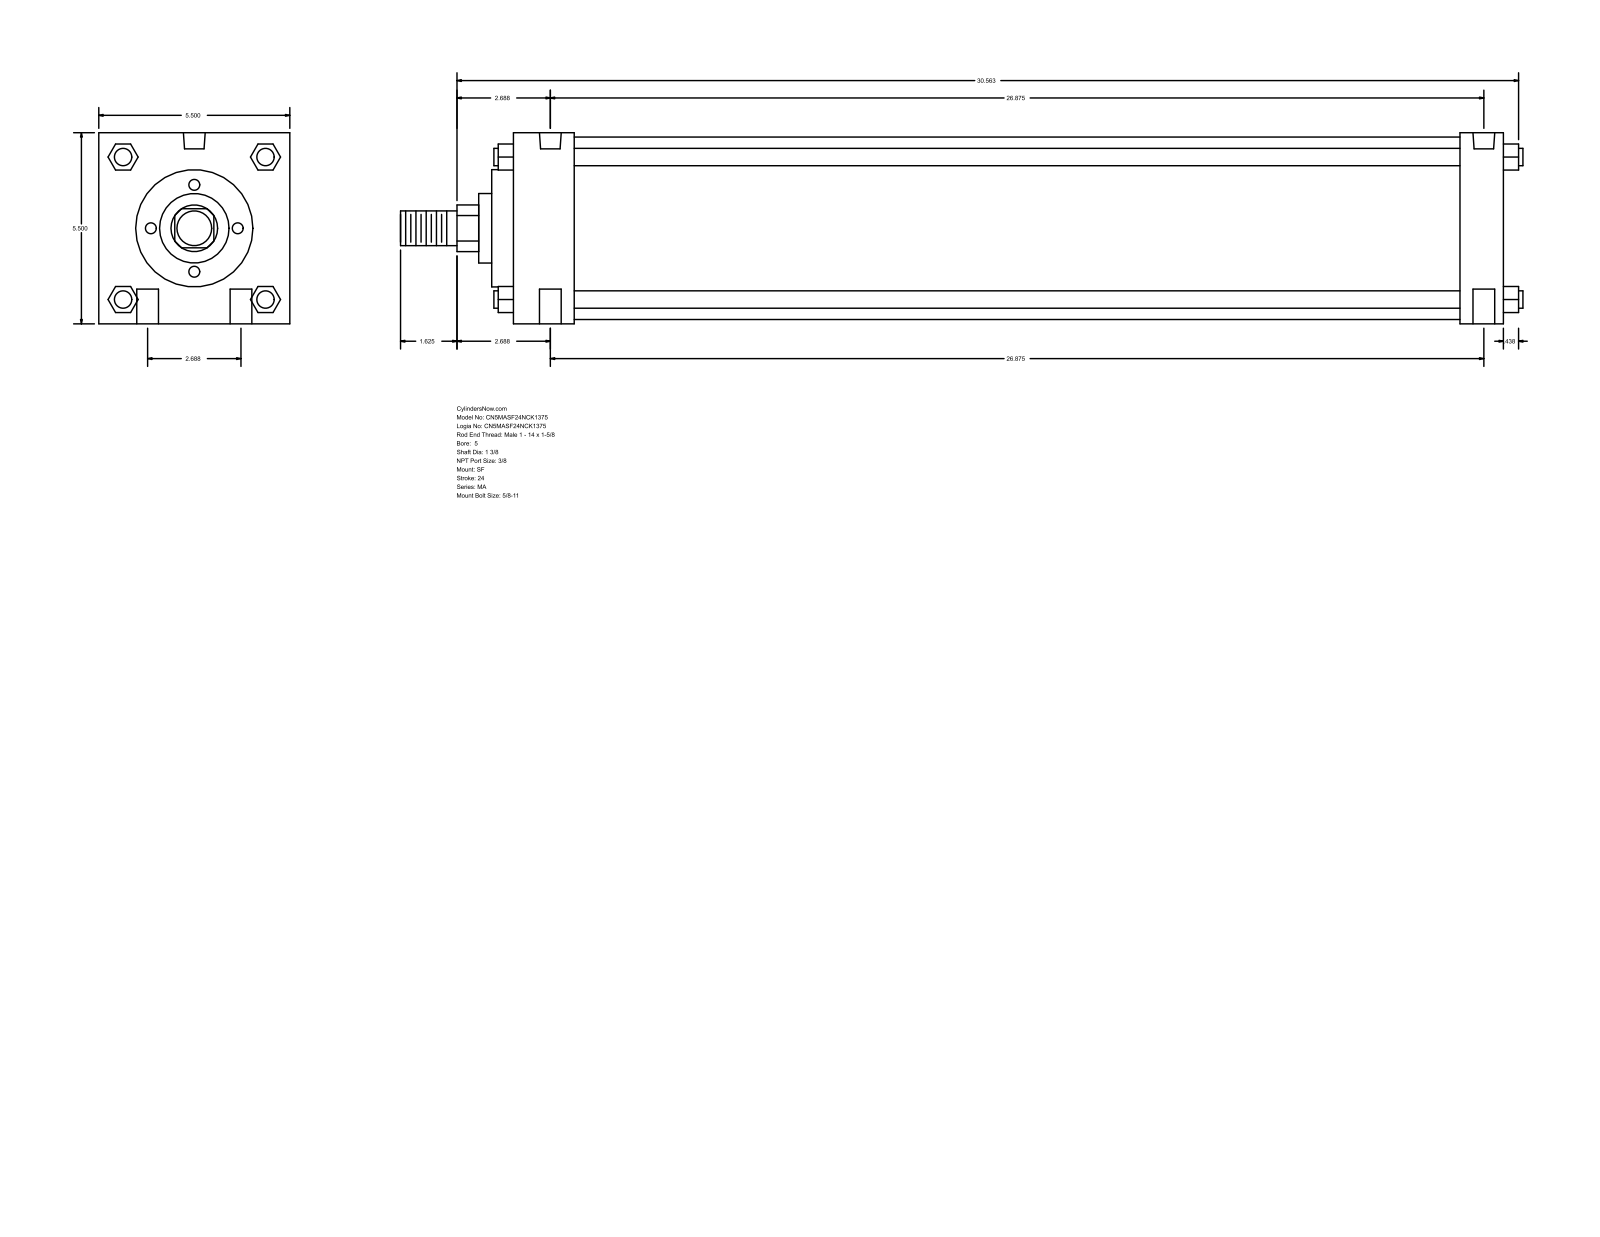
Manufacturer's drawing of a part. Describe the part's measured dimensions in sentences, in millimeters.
The part is named "MA_SF__0500_1.375". Its 3-D file was written by "GSSL Pune (CONFIG_CONTROL_DESIGN)". It is 0 solids with 126 faces: 95 planar, 31 cylindrical and 0 other. Overall it measures 820.74 by 139.7 by 139.7 millimeters. Round holes: 4 of diameter 15.88, 2 of diameter 11.11, 2 of diameter 15.93. Round bosses or shafts: 4 of diameter 12.7, 1 of diameter 133.35, 1 of diameter 85.72, 1 of diameter 50.8, 1 of diameter 34.92, 1 of diameter 25.4. Partial cylindrical surfaces (rounded edges, fillets, slot ends): 1 of radius 17.06. The main face-to-face distances are 139.7, 723.9, 44.45, 692.15, 647.7, 679.45, 31.75, 15.87, 60.32, 708.02. The hole center spacings are 34.13, 683.48, 682.63, 68.26, 686.03, 673.09.
